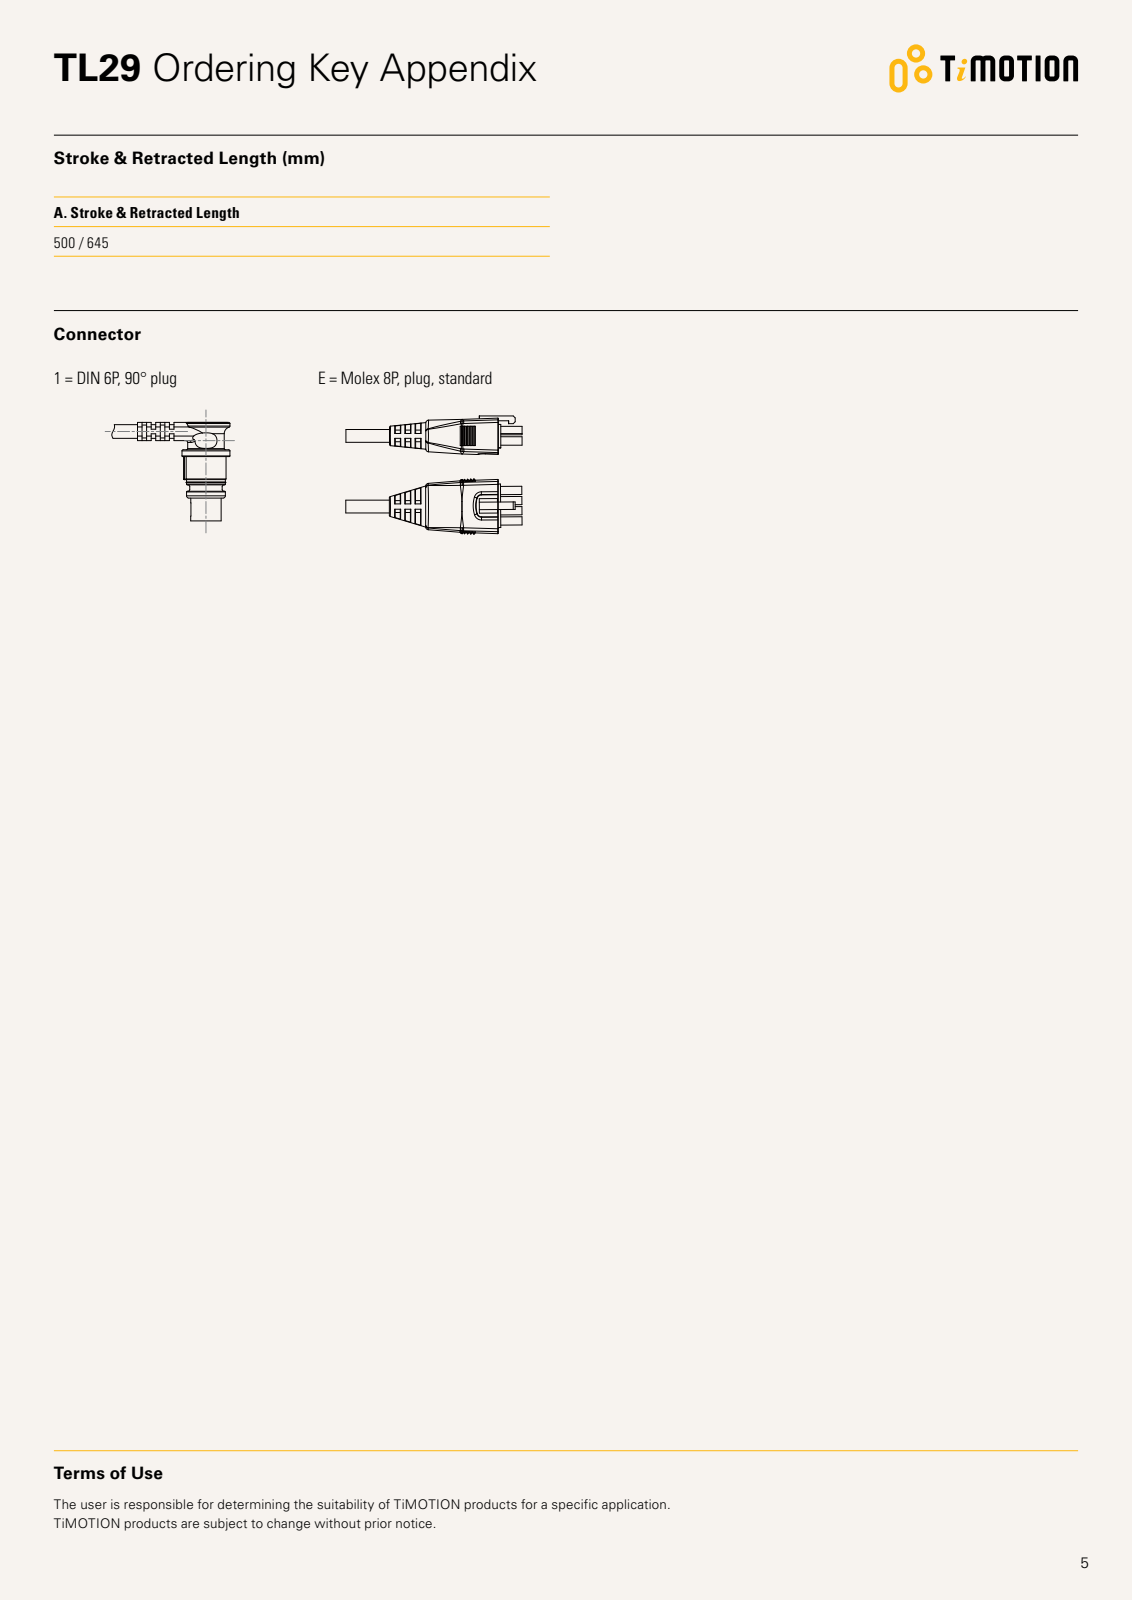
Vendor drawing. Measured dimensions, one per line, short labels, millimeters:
name: 產品三維模型圖-TL29(標準）-A
written by: SolidWorks 2015 (AUTOMOTIVE_DESIGN)
unit: mm
bodies: 2 solids, 304 faces (163 planar, 109 cylindrical, 32 other)
size: 645 × 183 × 107
volume: 3 167 000 mm³; area: 245 241 mm²
holes: 4× ⌀3.2, 4× ⌀5, 4× ⌀8, 4× ⌀8.5, 2× ⌀8.6, 1× ⌀4, 1× ⌀50, 1× ⌀60
bosses: 4× ⌀3, 2× ⌀8.2, 2× ⌀4.2, 1× ⌀70, 1× ⌀62, 1× ⌀12, 1× ⌀7, 1× ⌀5.5
rounds: 6× R1, 3× R2.5, 3× R6, 1× R3, 1× R3.75, 1× R8.5, 1× R27
face distances: 40, 2.5, 42.5, 50.5, 10.5, 8, 4, 105, 46.5, 6.5
hole spacings: 16.16, 21.21, 28.3, 30, 9, 22.17, 33.15, 39.45
